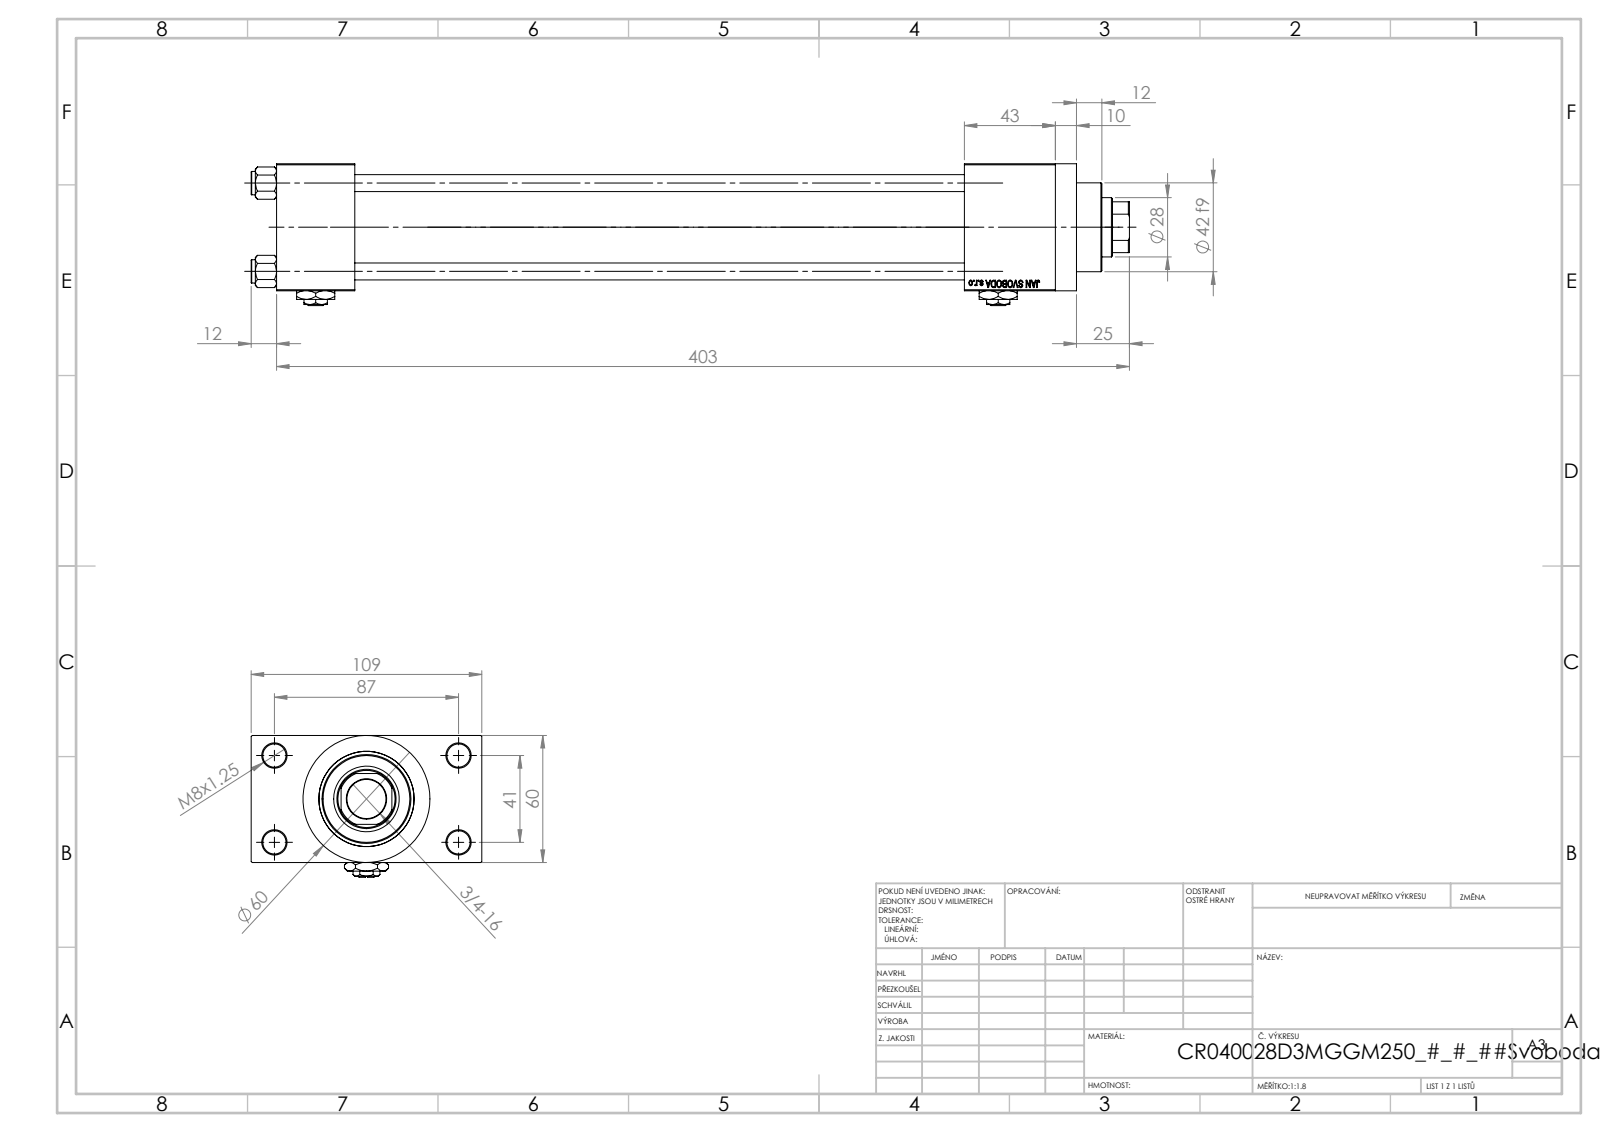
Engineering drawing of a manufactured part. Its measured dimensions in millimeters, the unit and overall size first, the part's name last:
Units: millimetres
Overall size (bounding box): 415 × 109 × 67
Round holes (diameter × count): ⌀8 ×4, ⌀11 ×4, ⌀7 ×2, ⌀16.66 ×2, ⌀24 ×2, ⌀18.5 ×1, ⌀28 ×1, ⌀31 ×1, ⌀40 ×1, ⌀45 ×1
Round bosses / shafts (diameter × count): ⌀11 ×4, ⌀60 ×1, ⌀46 ×1, ⌀42 ×1
Partial cylindrical surfaces — rounded edges, fillets, slot ends (radius × count): R13.5 ×1
Main face-to-face distances: 60, 24.5, 84.5, 288, 37, 325, 368, 331, 43, 109
Hole centre spacings: 22.65, 29.49, 41.7, 47.15, 48.09, 64.35, 76.49, 41
Volume: 813 024 mm³ · Surface area: 235 970 mm²
Bodies: 13 solids, 1206 faces (546 planar, 100 cylindrical, 560 other)
Part name (STEP PRODUCT): V215CR_D_TYCINKA; Zatka_pro_OIL_PORT; V215CR_VCP_D; V215_VC_A (+2 more)
STEP written by: SolidWorks 2019 (CONFIG_CONTROL_DESIGN)
